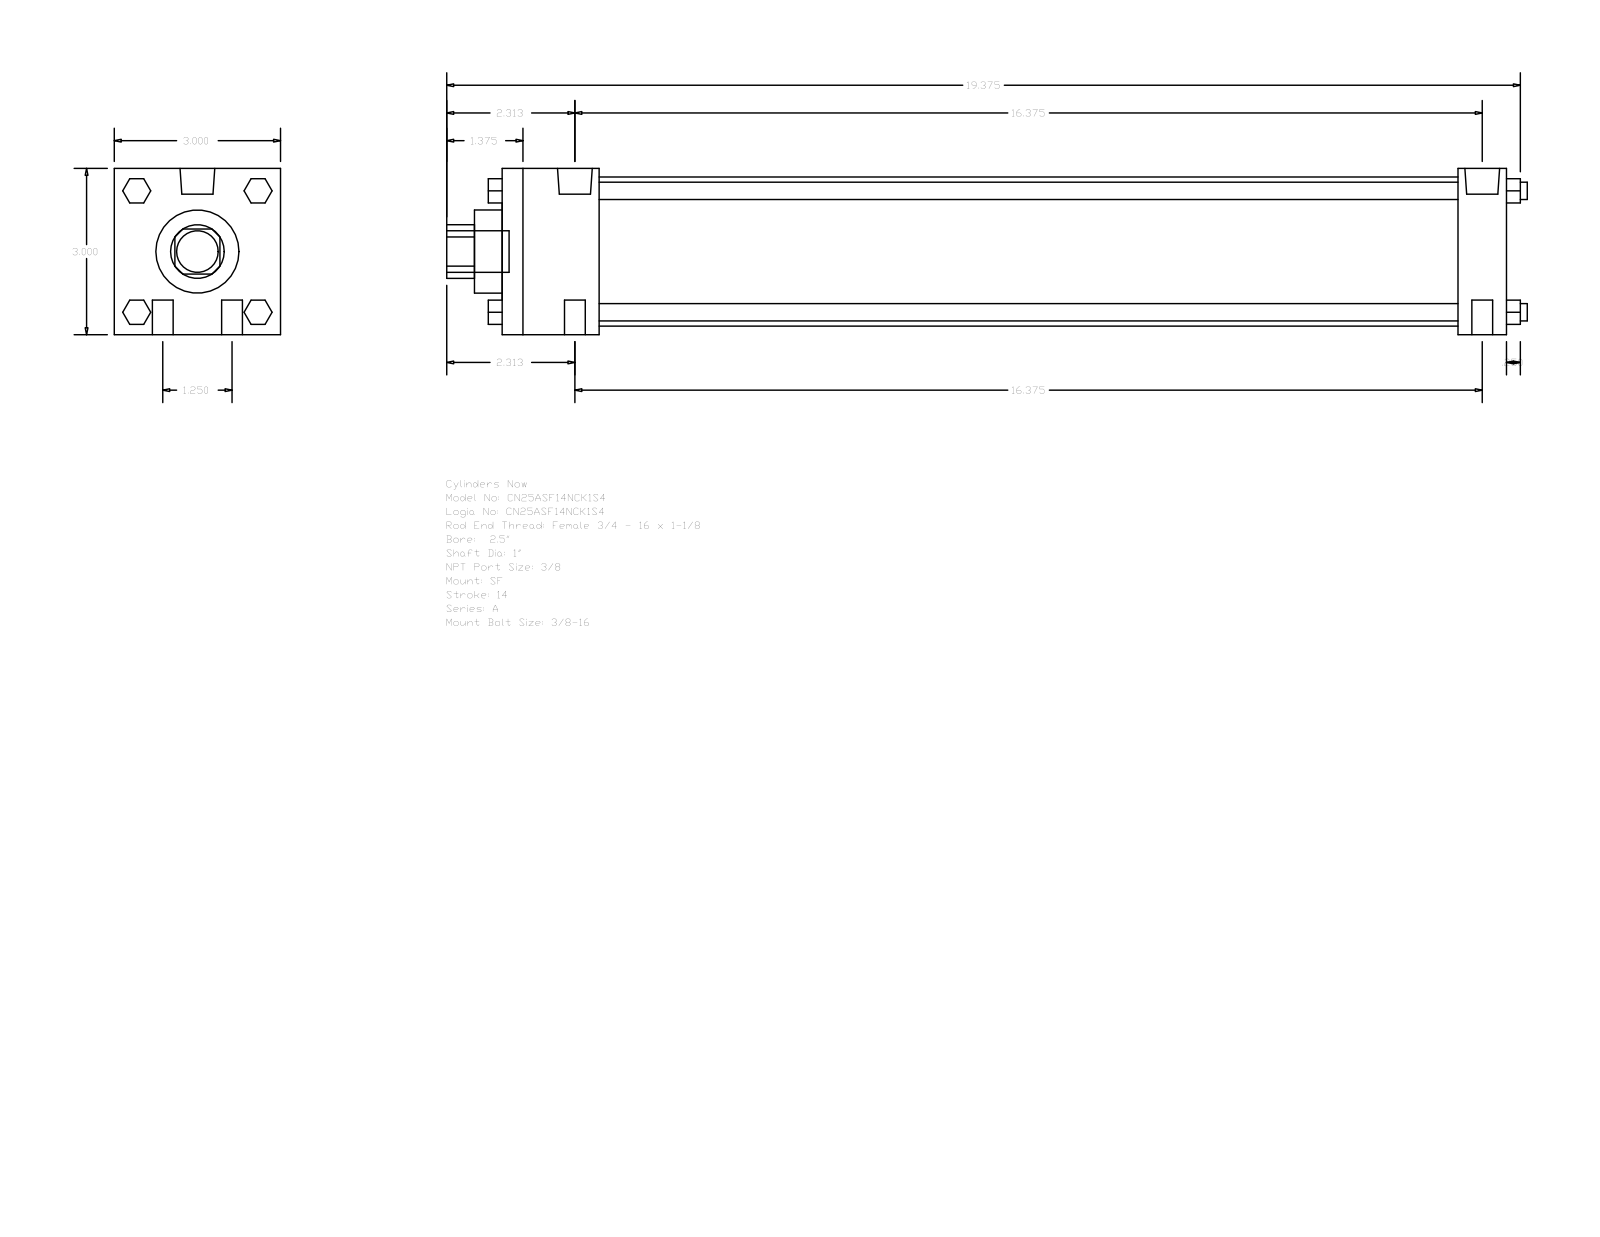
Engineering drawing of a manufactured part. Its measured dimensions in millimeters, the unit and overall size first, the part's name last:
Units: millimetres
Overall size (bounding box): 495.3 × 76.2 × 76.2
Round holes (diameter × count): ⌀25.4 ×1, ⌀38.1 ×1, ⌀68.33 ×1
Round bosses / shafts (diameter × count): ⌀9.53 ×4, ⌀7.94 ×4, ⌀15.93 ×2, ⌀5.56 ×2, ⌀19.05 ×1
Partial cylindrical surfaces — rounded edges, fillets, slot ends (radius × count): R12.29 ×1
Main face-to-face distances: 76.2, 460.37, 438.15, 22.22, 44.45, 393.7, 415.92, 12.7, 473.07, 6.35
Bodies: 0 solids, 124 faces (94 planar, 30 cylindrical, 0 other)
Part name (STEP PRODUCT): A_SF__0250_1
STEP written by: GSSL Pune (CONFIG_CONTROL_DESIGN)
